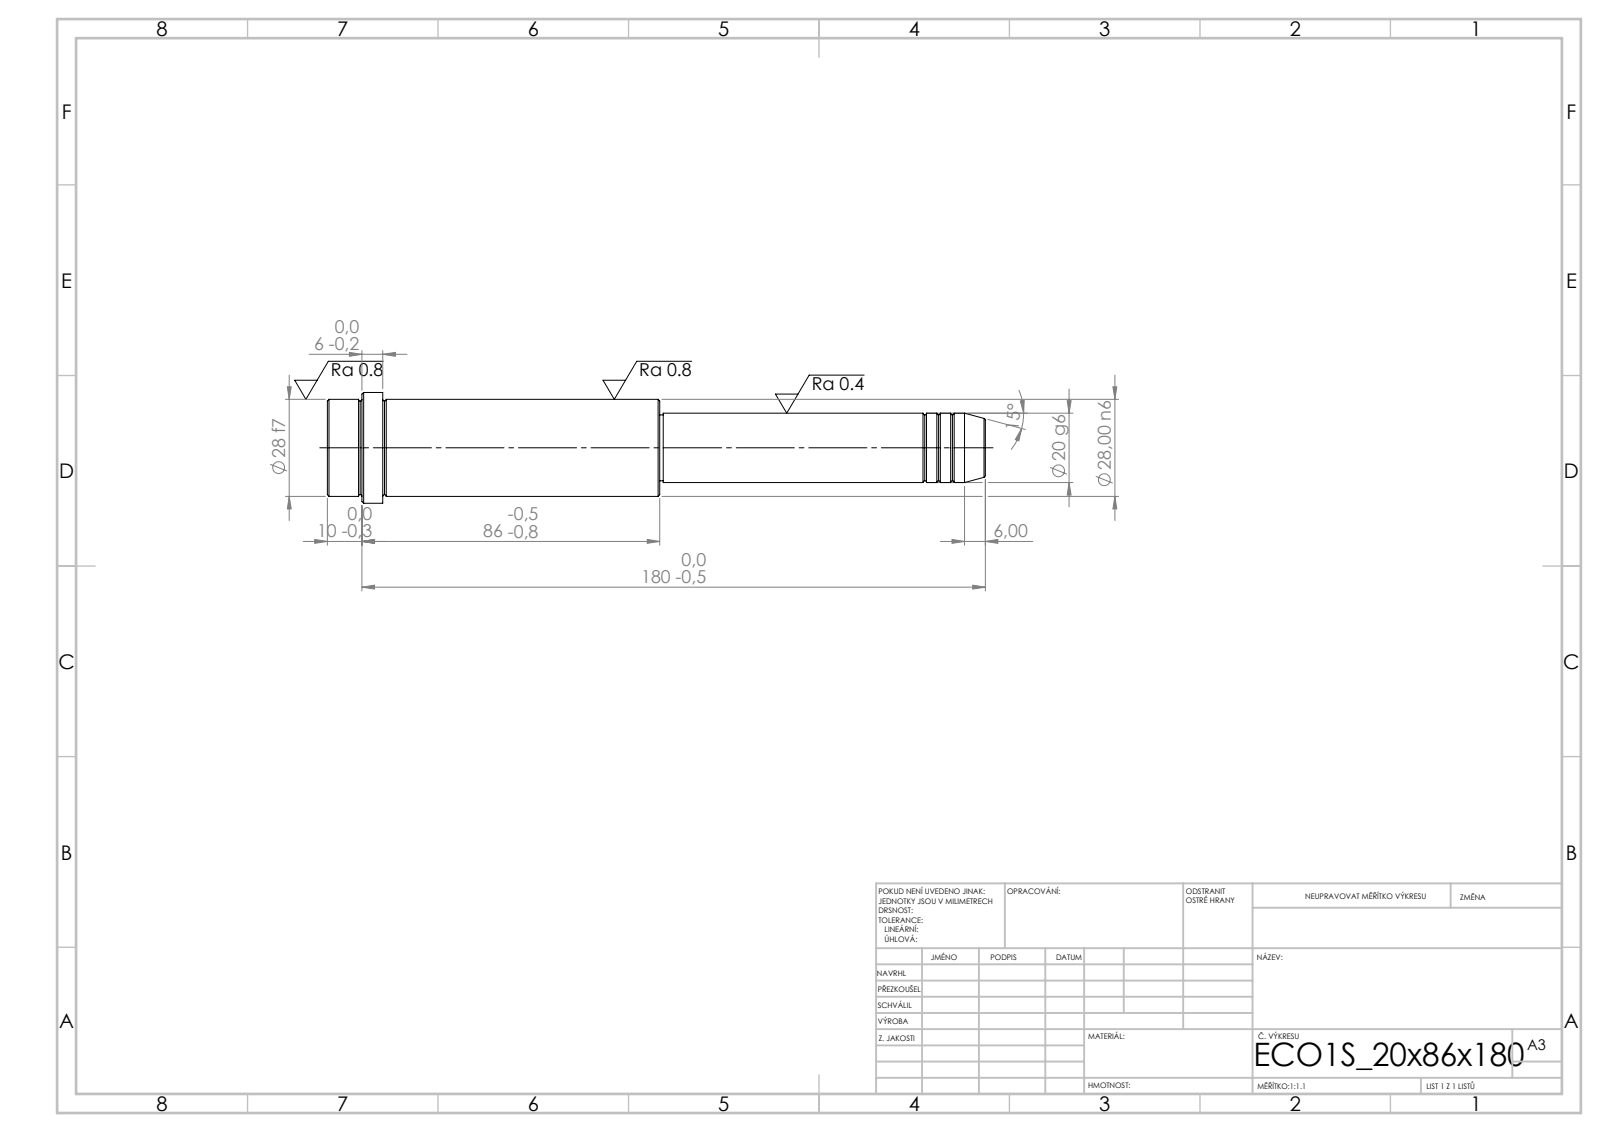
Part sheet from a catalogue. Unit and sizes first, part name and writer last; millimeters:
Units: millimetres
Overall size (bounding box): 190 × 32 × 32
Round bosses / shafts (diameter × count): ⌀32 ×1, ⌀28 ×1, ⌀20 ×1, ⌀19 ×1
Main face-to-face distances: 96, 94, 190, 174, 80, 16, 180, 86, 6, 10
Volume: 89 281 mm³ · Surface area: 16 086 mm²
Bodies: 1 solid, 52 faces (6 planar, 16 cylindrical, 30 other)
STEP written by: SolidWorks 2019 (CONFIG_CONTROL_DESIGN)
